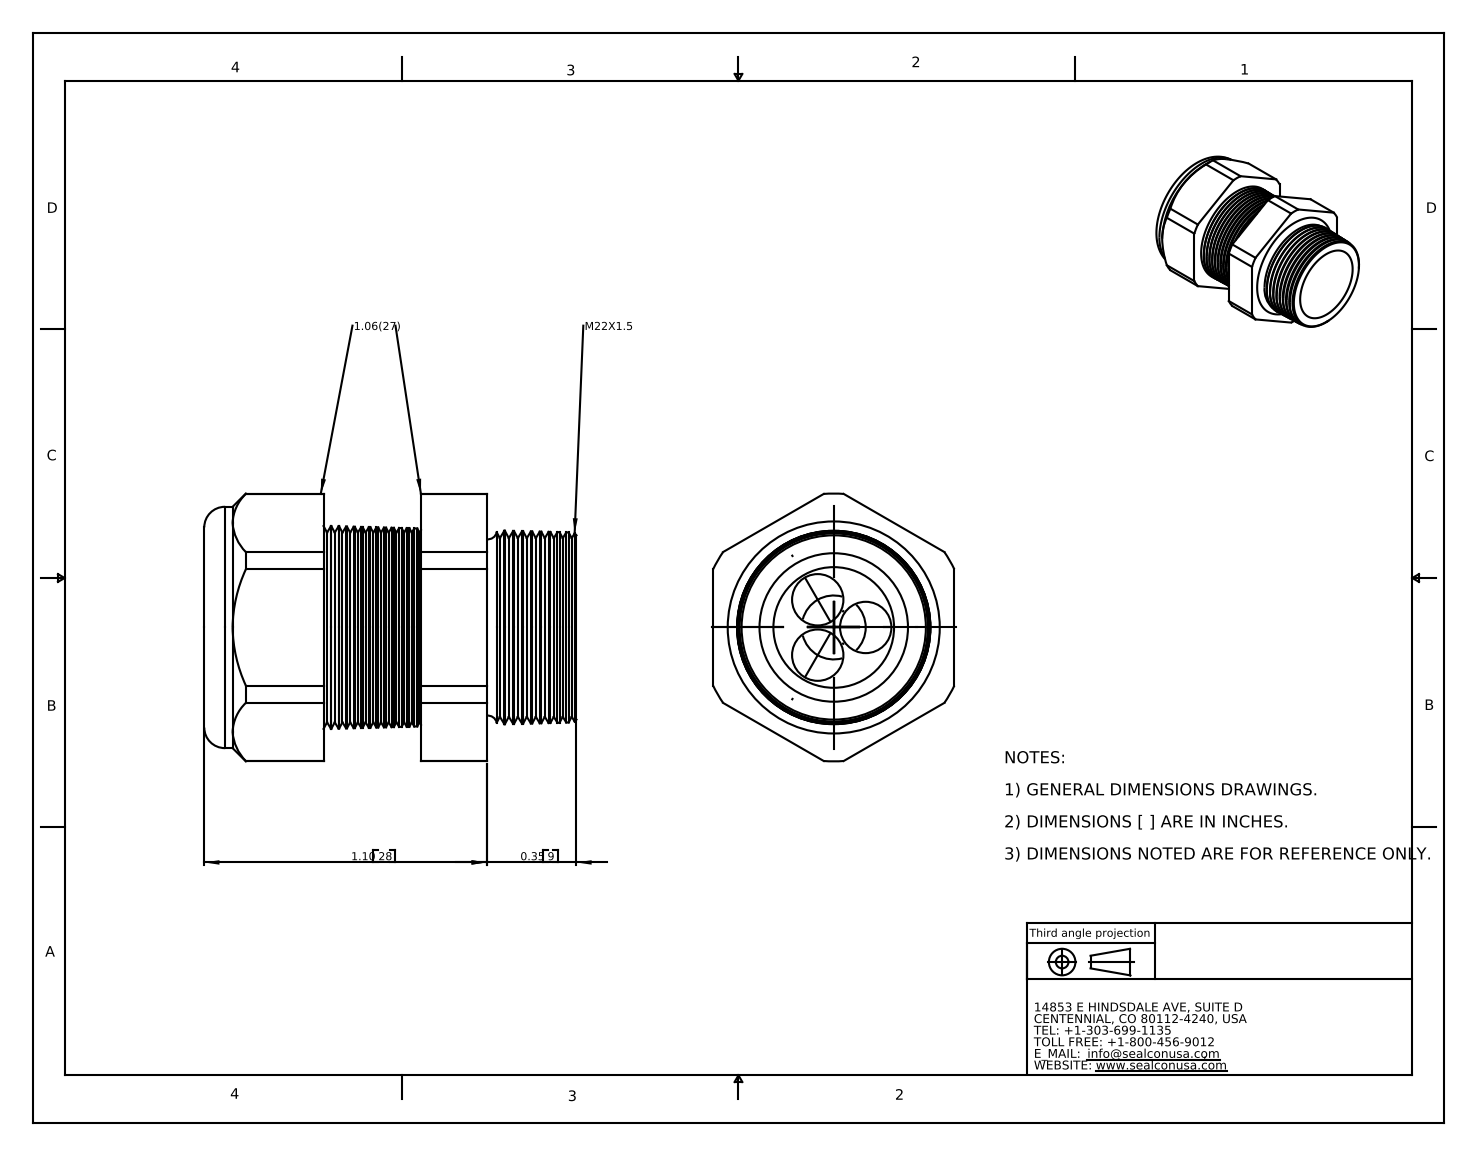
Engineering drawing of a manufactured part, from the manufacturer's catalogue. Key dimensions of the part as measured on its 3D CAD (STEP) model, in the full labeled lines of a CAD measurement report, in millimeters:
Part name (STEP PRODUCT): CD22M7-BK
STEP written by: SolidWorks 2007 (CONFIG_CONTROL_DESIGN)
Units: millimetres
Bodies: 2 solids, 192 faces (20 planar, 26 cylindrical, 146 other)
Overall size (bounding box): 36.8 × 26.5 × 23.9
Volume: 9 390 mm³ · Surface area: 6 626 mm²
Round holes (diameter × count): ⌀5.1 ×3, ⌀11.4 ×1, ⌀11.9 ×1
Round bosses / shafts (diameter × count): ⌀23.9 ×1
Partial cylindrical surfaces — rounded edges, fillets, slot ends (radius × count): R13.3 ×1
Main face-to-face distances: 23.9, 21.4, 11.8, 9.7, 27.9, 16.1, 6.5, 36.8, 25, 15.4
Hole centre spacings: 3.1, 5.5, 5.5
